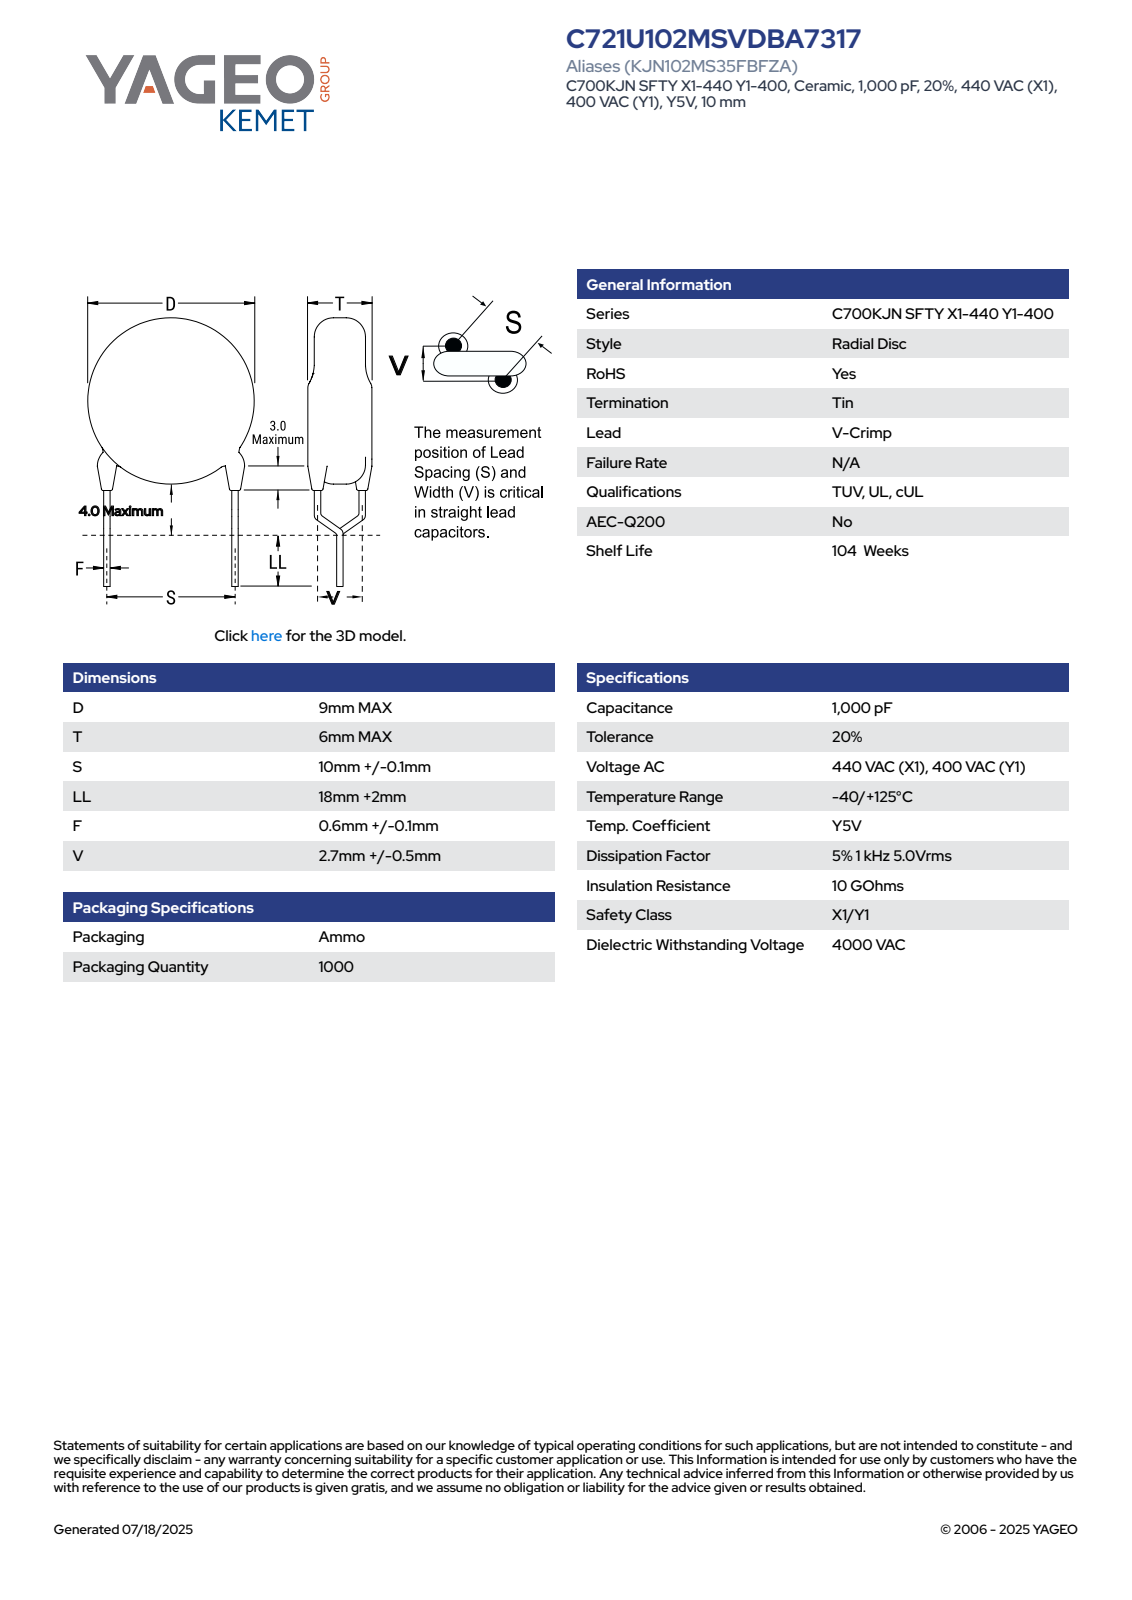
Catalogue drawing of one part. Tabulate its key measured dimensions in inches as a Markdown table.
| quantity | value |
| --- | --- |
| part name | CCD_VC9X6_D9T6S10LL20F0.7V2.7 |
| STEP written by | SolidWorks 2021 (AUTOMOTIVE_DESIGN) |
| units | inches |
| bodies | 4 solids, 89 faces (63 planar, 22 cylindrical, 4 other) |
| overall size | 1.142 × 0.441 × 0.236 |
| volume | 0.024 in³ |
| surface area | 0.606 in² |
| round bosses / shafts (diameter × count) | 0.028 × 6, 0.047 × 4, 0.354 × 1 |
| main face-to-face distances | 0.236, 0.787, 0.043, 0.993, 0.206, 0.95, 0.162, 0.035, 0.027, 0.088 |
